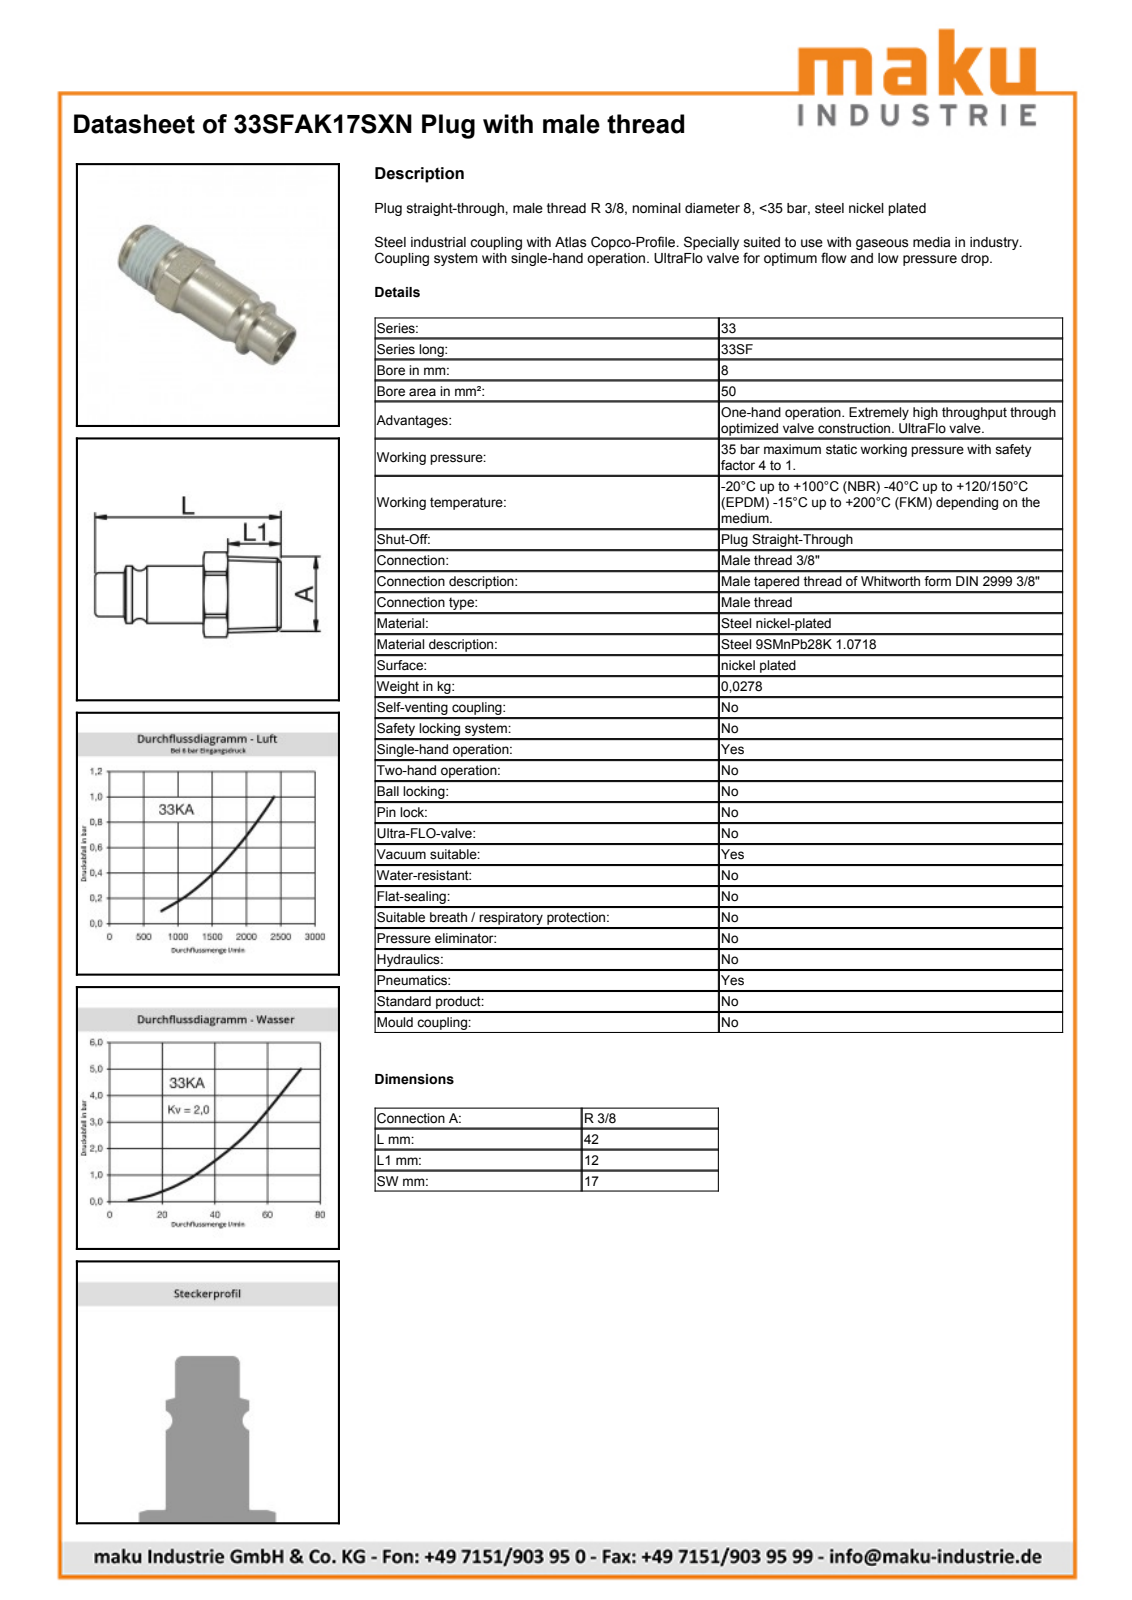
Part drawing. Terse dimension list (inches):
name: D110730
written by: Autodesk Inventor 2013 (AUTOMOTIVE_DESIGN)
unit: in
bodies: 1 solid, 39 faces (9 planar, 11 cylindrical, 19 other)
size: 1.654 × 0.754 × 0.669
volume: 0.236 in³; area: 5.233 in²
holes: 1× ⌀0.307, 1× ⌀0.453
bosses: 1× ⌀0.508, 1× ⌀0.39
rounds: 1× R0.377
face distances: 0.669, 0.689, 0.965, 1.654
